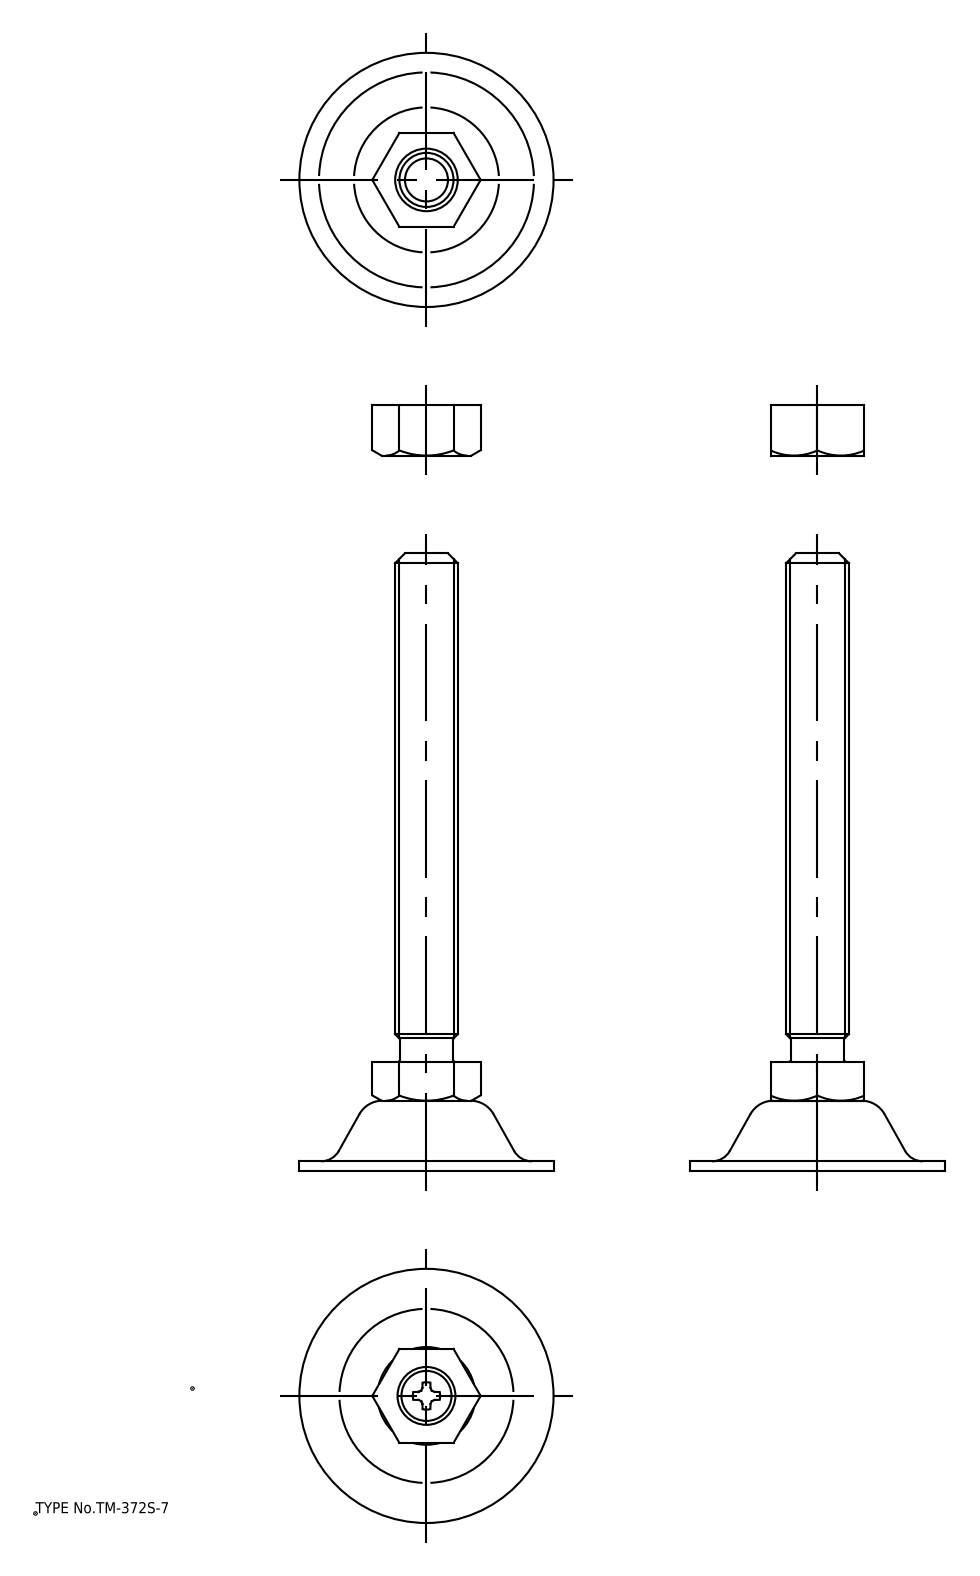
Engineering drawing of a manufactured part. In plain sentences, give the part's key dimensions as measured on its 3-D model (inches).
The part is named "アジャストボルト; ナット; フット". Its 3-D file was written by "spGate 18.9.1 (****-****-****-****) (AUTOMOTIVE_DESIGN)". It is 3 solids with 90 faces: 48 planar, 18 cylindrical and 24 other. Overall it measures 6.22 by 2.559 by 2.559 inches. Its volume is 3.034 cubic inches and its surface area 32.6 square inches. Round holes: 1 of diameter 0.583, 1 of diameter 0.63. Round bosses or shafts: 1 of diameter 2.559, 1 of diameter 0.531. Partial cylindrical surfaces (rounded edges, fillets, slot ends): 1 of radius 0.138. The main face-to-face distances are 0.945, 0.098, 0.512, 0.61, 2.815, 0.157, 0.709, 0.059, 0.551, 2.717.
